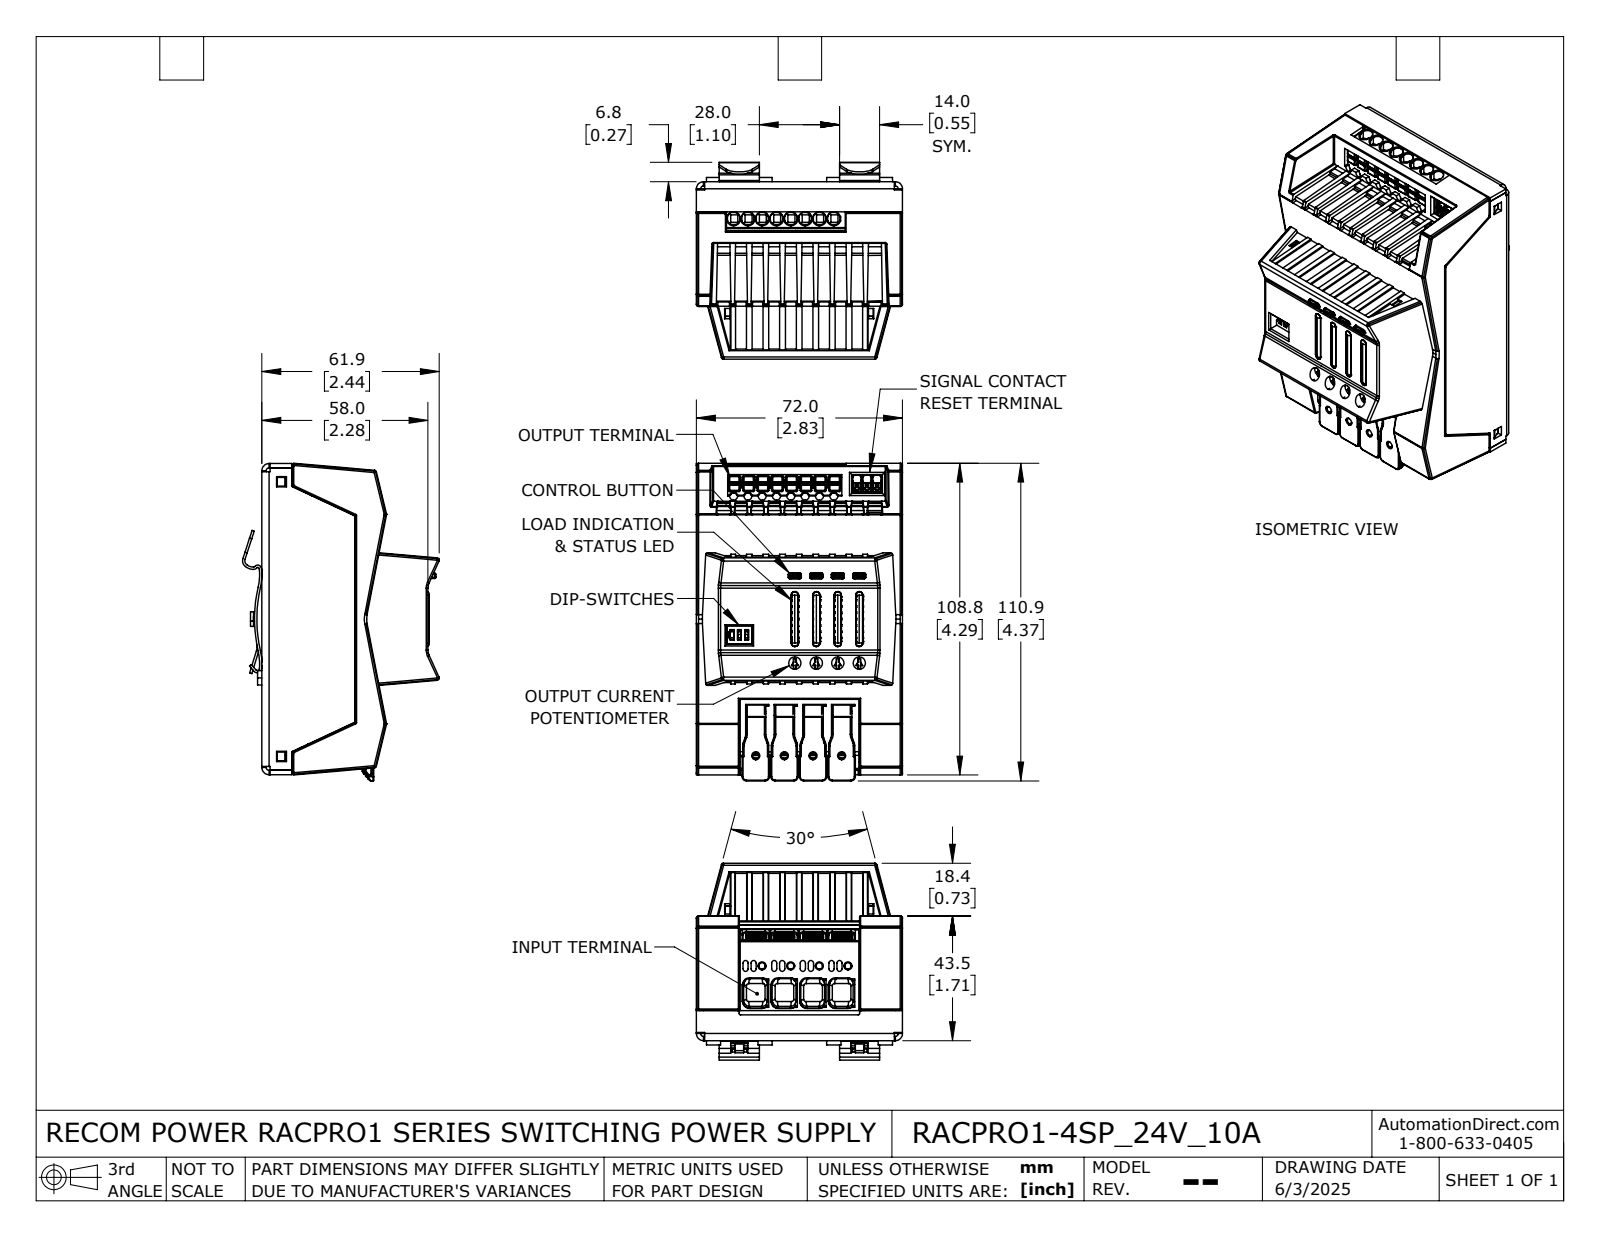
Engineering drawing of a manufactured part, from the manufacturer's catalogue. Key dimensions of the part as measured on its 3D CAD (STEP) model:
Part name (STEP PRODUCT): RACPRO1-4SP_24V_10A
STEP written by: SolidWorks 2024 (AUTOMOTIVE_DESIGN)
Units: inches
Bodies: 3 solids, 5752 faces (2742 planar, 1803 cylindrical, 1207 other)
Overall size (bounding box): 4.367 × 2.835 × 2.704
Volume: 20.07 in³ · Surface area: 131.4 in²
Round holes (diameter × count): ⌀0.087 ×8, ⌀0.177 ×8, ⌀0.079 ×6, ⌀0.169 ×6, ⌀0.134 ×3, ⌀0.067 ×2, ⌀0.075 ×2, ⌀0.138 ×2, ⌀0.044 ×1, ⌀0.048 ×1, ⌀0.059 ×1
Round bosses / shafts (diameter × count): ⌀0.197 ×4, ⌀0.079 ×4, ⌀0.201 ×2, ⌀0.074 ×2, ⌀0.043 ×1, ⌀0.039 ×1
Partial cylindrical surfaces — rounded edges, fillets, slot ends (radius × count): R0.012 ×140, R0.008 ×121, R0.016 ×88, R0.02 ×87, R0.031 ×47, R0.01 ×46, R0.039 ×36, R0.006 ×32
Main face-to-face distances: 0.059, 0.039, 0.098, 1.181, 1.22, 1.28, 1.283, 1.224, 1.185, 2.835
Hole centre spacings: 0.394, 0.787, 0.197, 0.591, 0.557, 0.652, 0.881, 1.181
